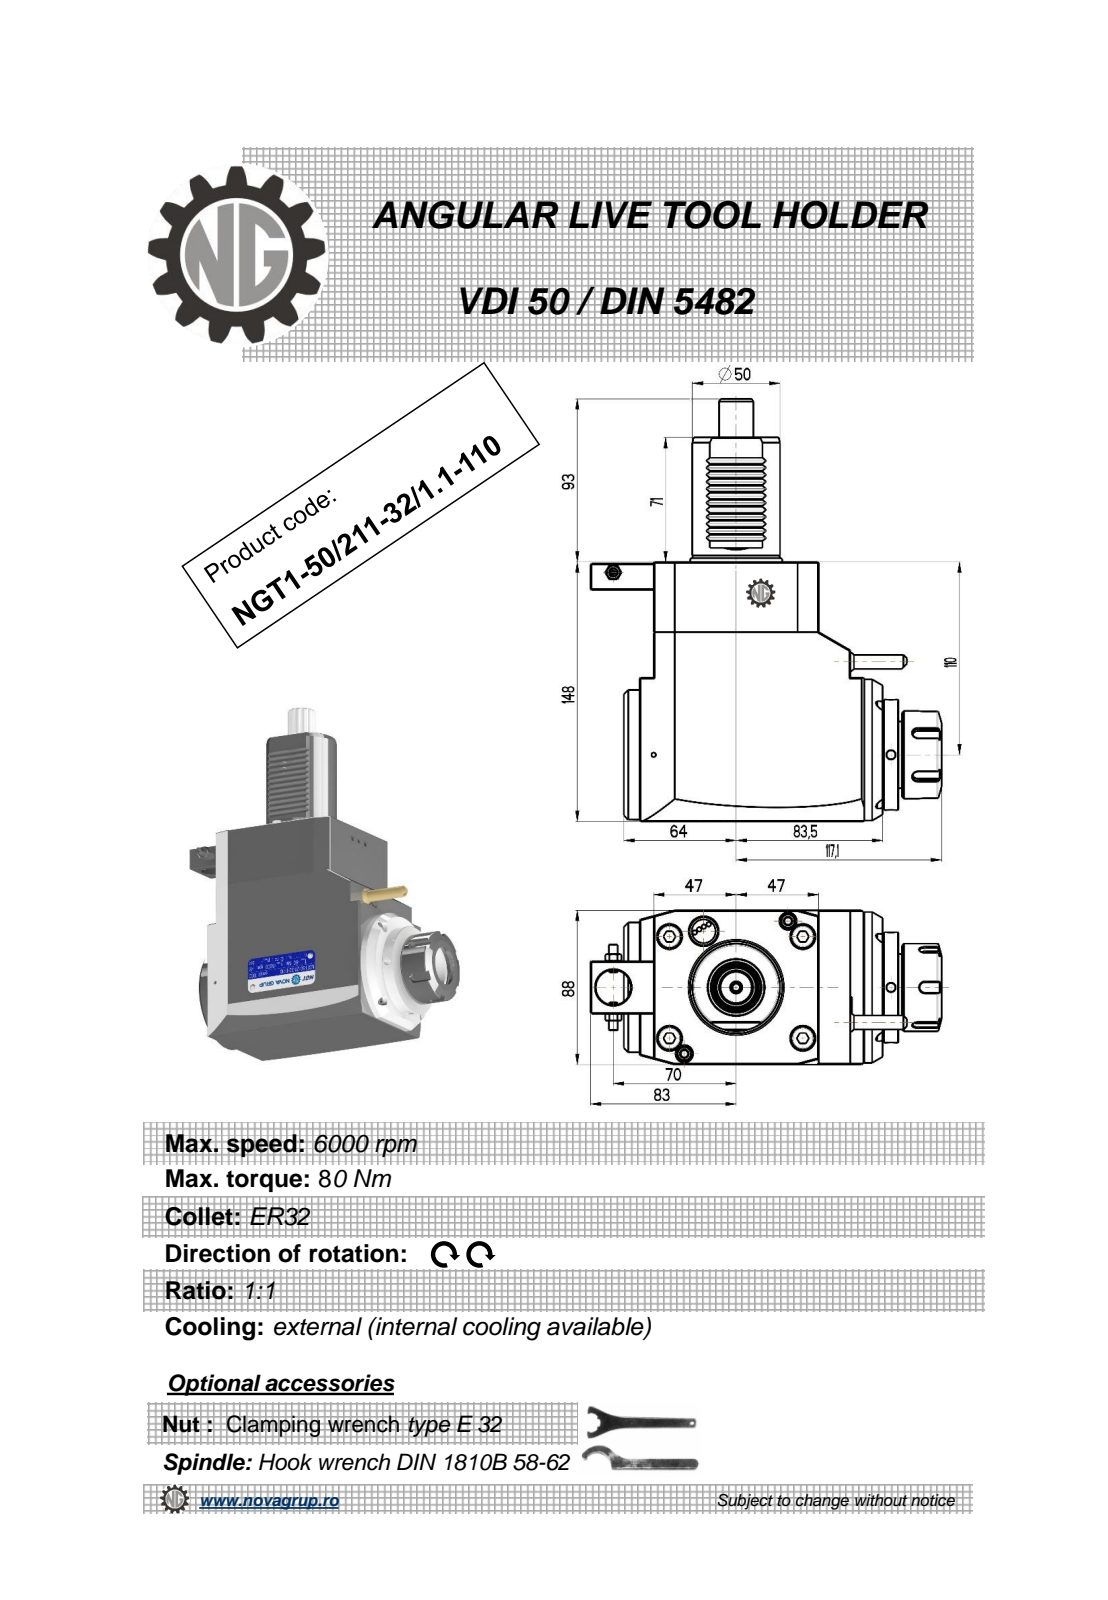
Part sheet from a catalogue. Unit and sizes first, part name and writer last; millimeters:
Units: millimetres
Overall size (bounding box): 241 × 200.1 × 88
Round holes (diameter × count): ⌀5 ×3, ⌀3 ×1, ⌀4.2 ×1, ⌀5.3 ×1, ⌀9.5 ×1, ⌀20 ×1, ⌀27 ×1
Round bosses / shafts (diameter × count): ⌀50 ×2, ⌀86 ×1, ⌀74 ×1, ⌀63 ×1, ⌀50.5 ×1, ⌀41 ×1, ⌀10 ×1, ⌀8.96 ×1
Partial cylindrical surfaces — rounded edges, fillets, slot ends (radius × count): R3.33 ×24, R0.26 ×12, R0.3 ×12, R0.2 ×6, R3 ×5, R2.5 ×1, R8.25 ×1, R9.75 ×1
Main face-to-face distances: 88, 148, 147.5, 9, 17, 8, 94, 111, 130.5, 36.5
Hole centre spacings: 52.46, 56.65, 70, 88.25, 101.5, 158.25
Volume: 1 799 000 mm³ · Surface area: 112 400 mm²
Bodies: 1 solid, 469 faces (190 planar, 137 cylindrical, 142 other)
Part name (STEP PRODUCT): NGT1_50_211_32_1_1_110
STEP written by: PRO/ENGINEER BY PARAMETRIC TECHNOLOGY CORPORATION, 2010280 (CONFIG_CONTROL_DESIGN)
